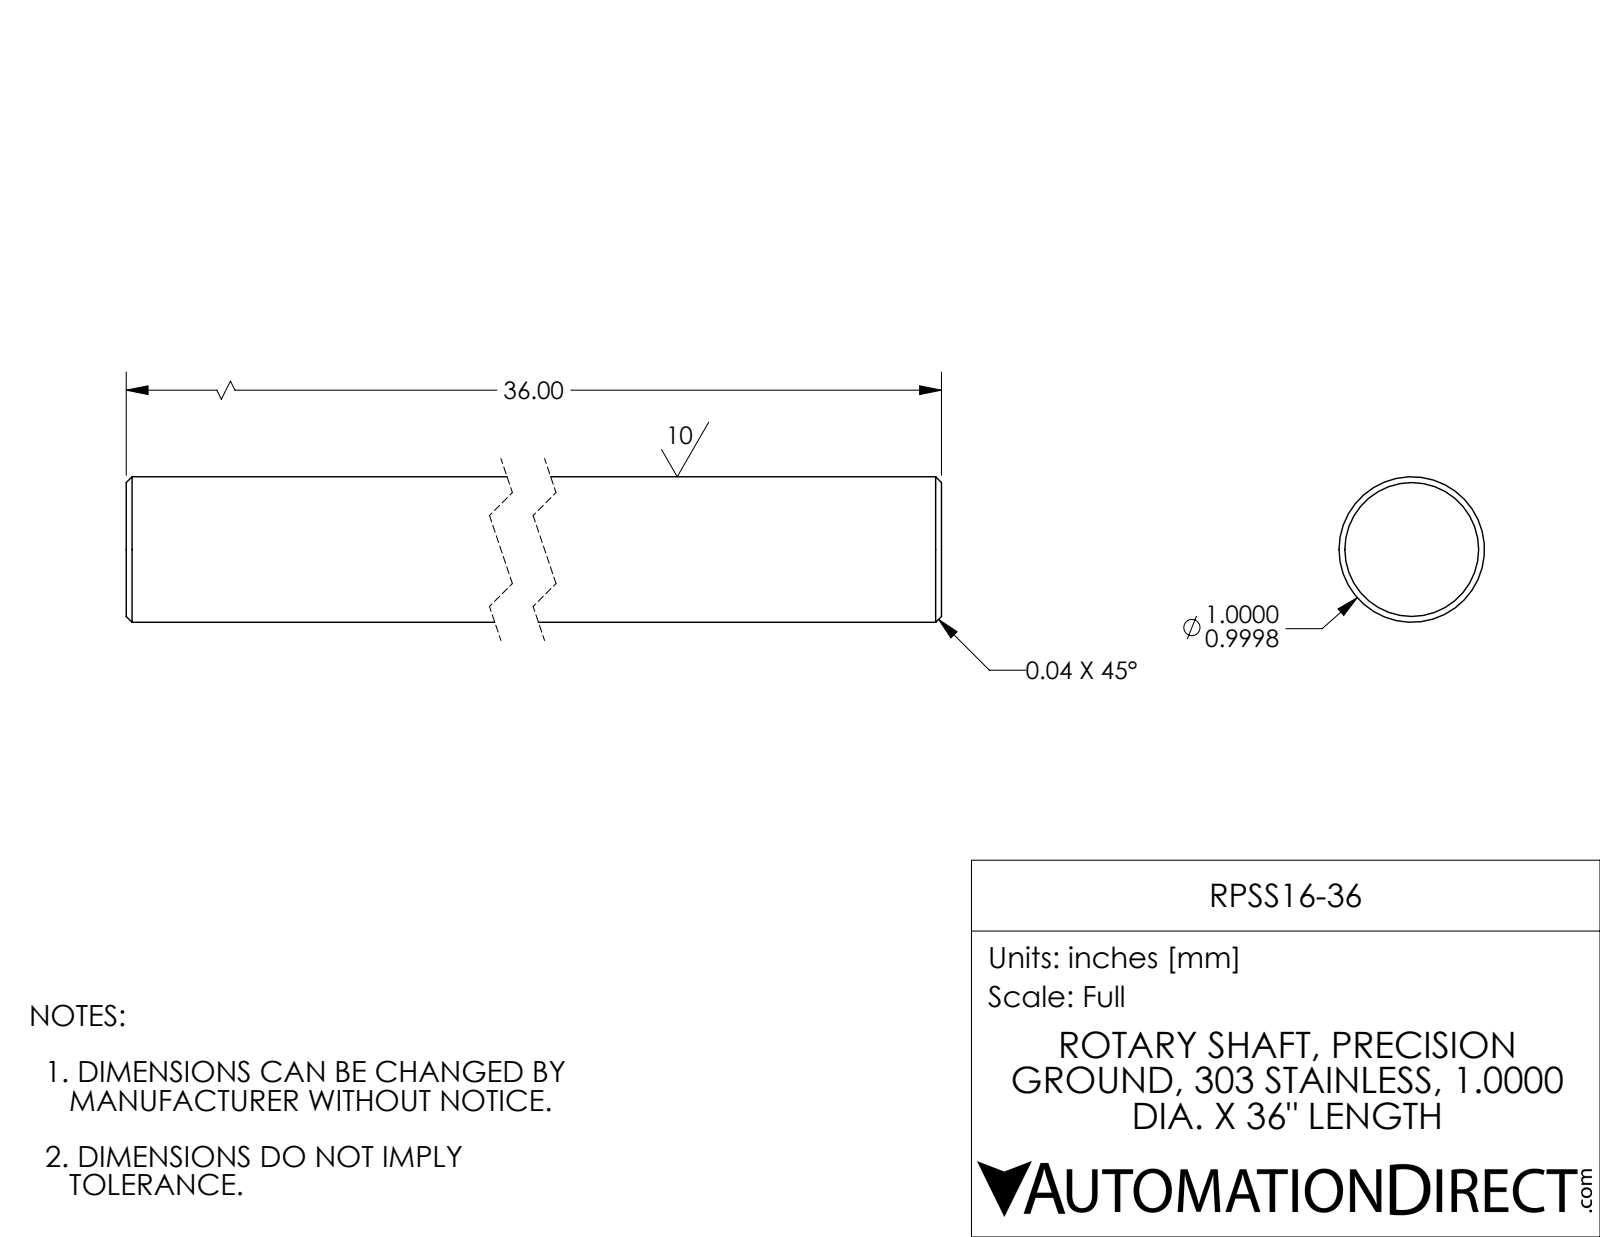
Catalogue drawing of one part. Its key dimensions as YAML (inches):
part_name: "RPSS16-36"
step_written_by: "SolidWorks 2017 (AUTOMOTIVE_DESIGN)"
units: inches
bodies: {solids: 1, faces: 8, planar: 2, cylindrical: 2, other: 4}
overall_size: [36, 1, 1]
volume: 28.27
surface_area: 114.5
round_bosses_or_shafts:
  - {diameter: 1, count: 1}
face_to_face_distances: [36]
